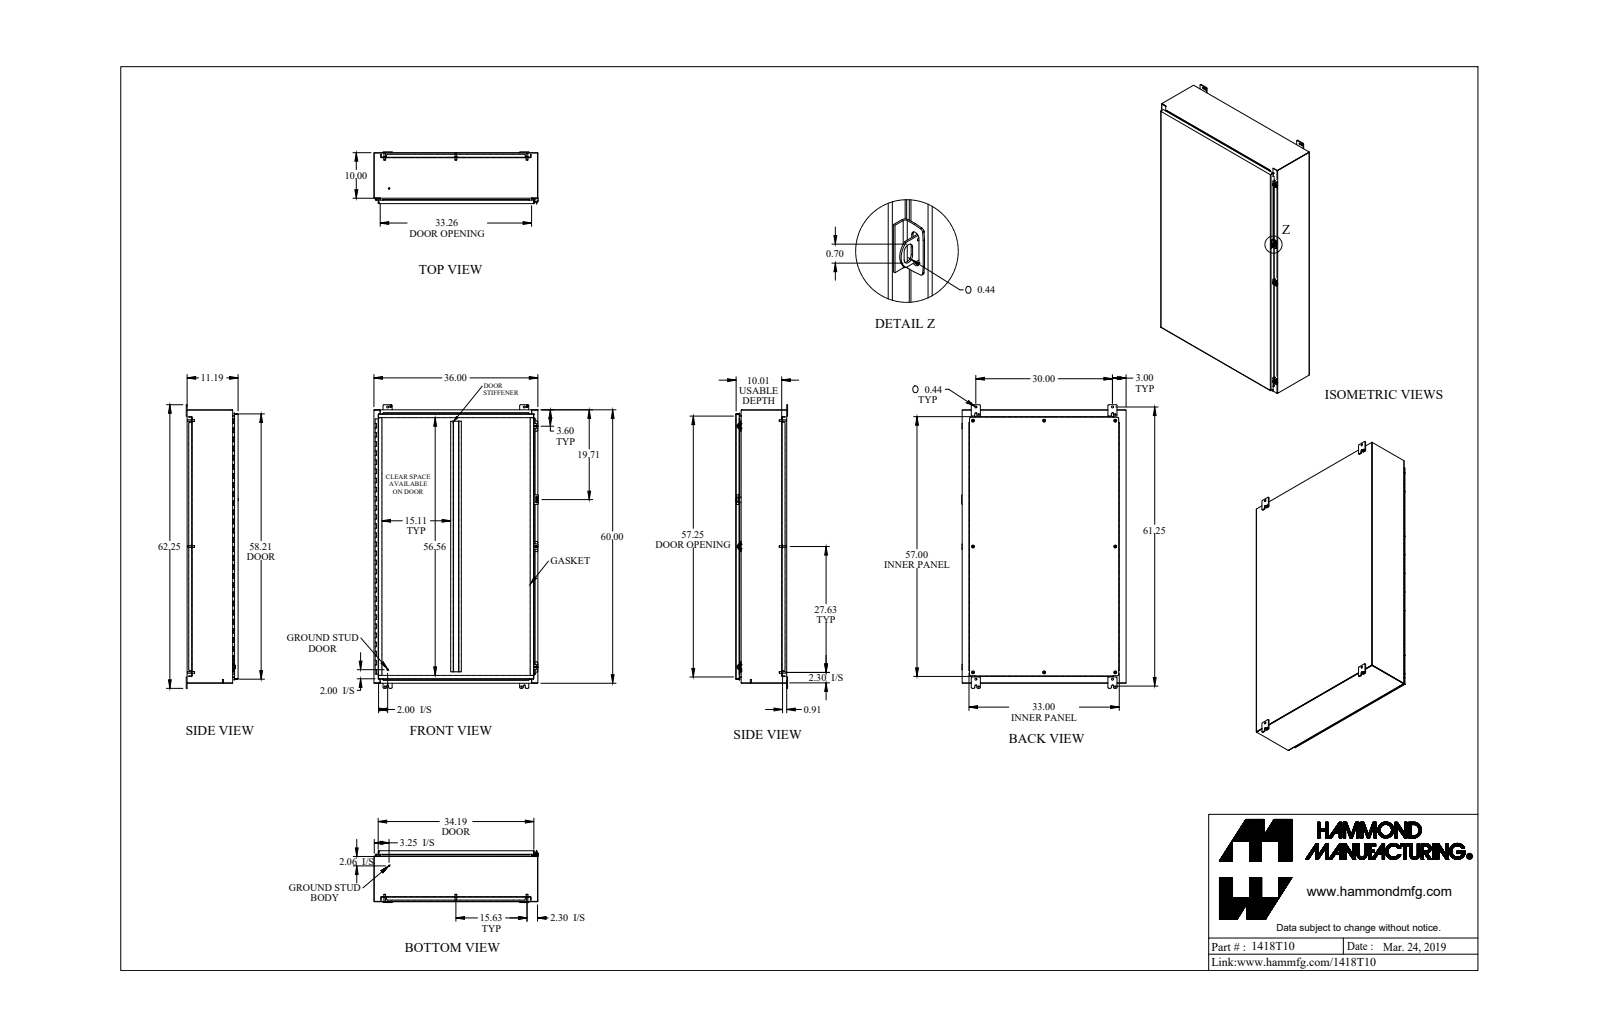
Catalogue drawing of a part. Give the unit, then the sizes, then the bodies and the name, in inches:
Units: inches
Overall size (bounding box): 62.25 × 36.125 × 11.437
Round holes (diameter × count): ⌀0.5 ×8, ⌀0.307 ×4, ⌀0.313 ×4, ⌀0.437 ×4, ⌀0.445 ×4, ⌀0.213 ×3, ⌀0.265 ×3, ⌀0.375 ×3, ⌀0.125 ×1, ⌀0.187 ×1
Round bosses / shafts (diameter × count): ⌀0.65 ×8, ⌀0.375 ×8, ⌀0.33 ×8, ⌀1 ×4, ⌀0.5 ×3, ⌀0.39 ×3, ⌀0.244 ×3, ⌀0.281 ×2
Partial cylindrical surfaces — rounded edges, fillets, slot ends (radius × count): R0.188 ×34, R0.036 ×22, R0.108 ×22, R0.25 ×20, R0.048 ×19, R0.143 ×19, R0.116 ×16, R0.125 ×8
Main face-to-face distances: 0.072, 11.113, 11.041, 0.937, 11.185, 0.095, 1.009, 10.081, 10.009, 1.032
Hole centre spacings: 15.625, 27.625, 57.417, 63.475, 30, 31.25, 41.71, 55.25
Volume: 745.1 in³ · Surface area: 19 289 in²
Bodies: 56 solids, 1796 faces (1043 planar, 675 cylindrical, 78 other)
Part name (STEP PRODUCT): 1418T10_Default
STEP written by: SolidWorks 2019 (CONFIG_CONTROL_DESIGN)
